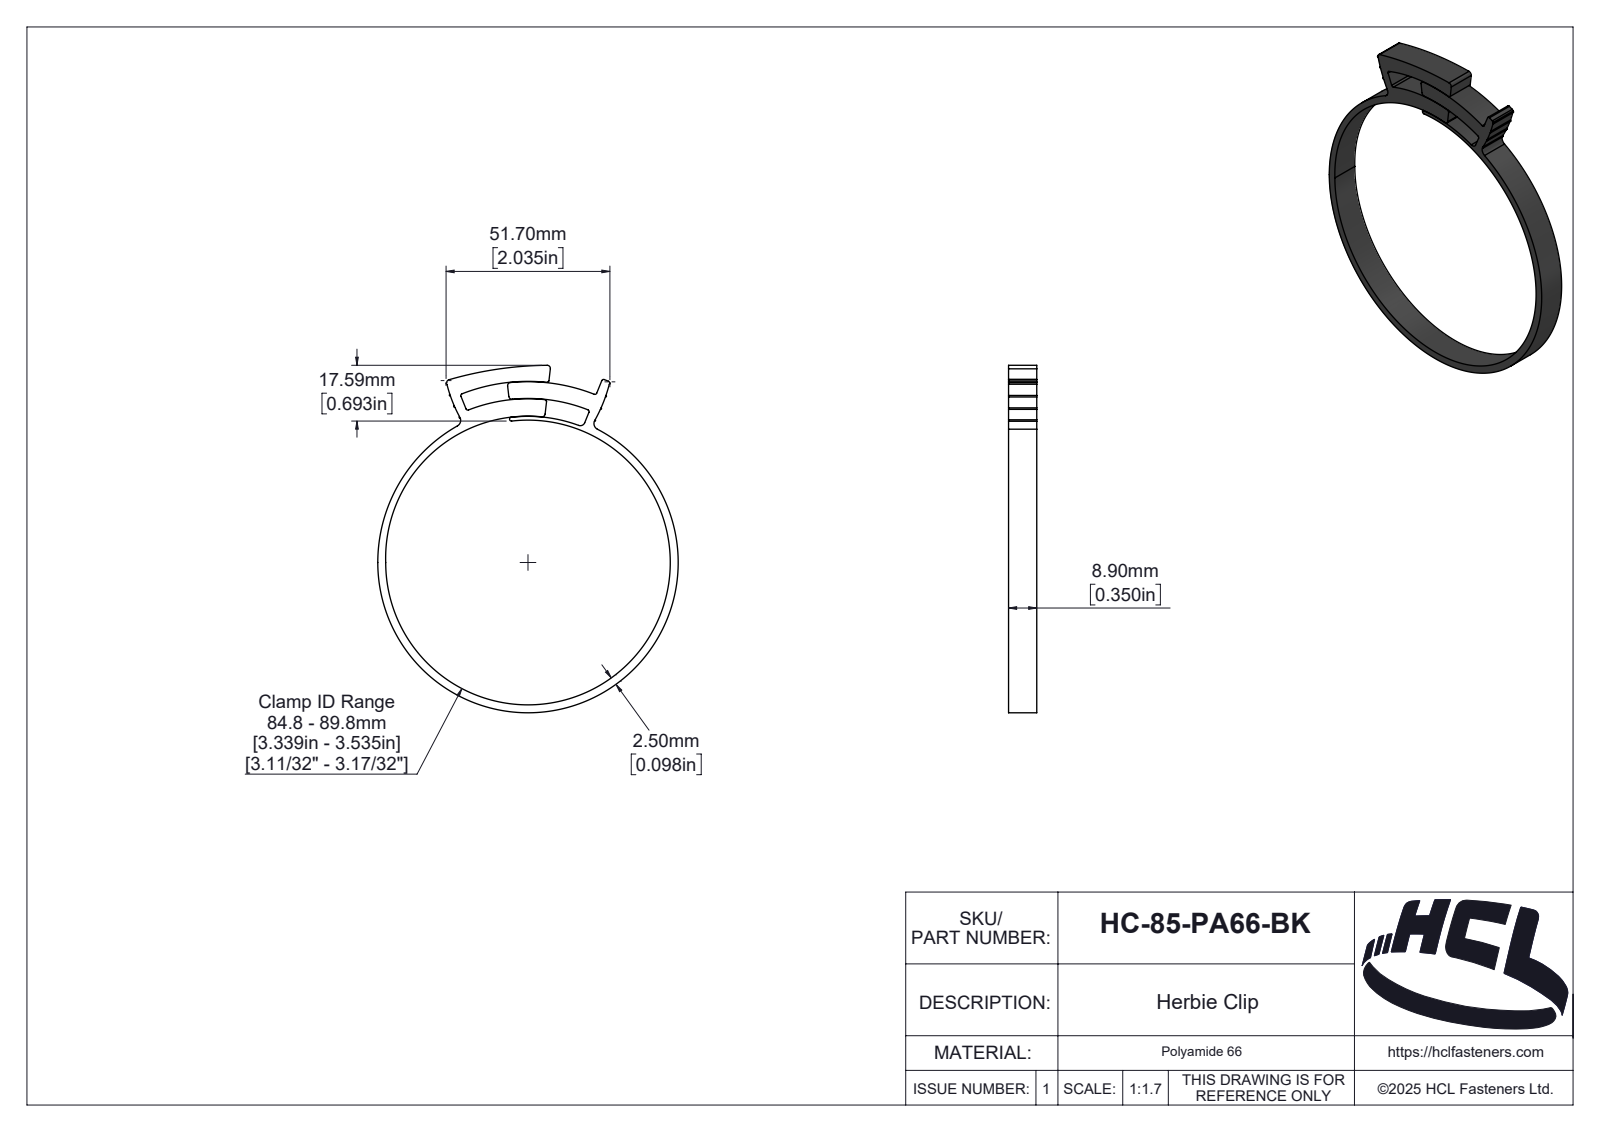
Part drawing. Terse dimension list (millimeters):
name: HC-85-PA66-BK
written by: SolidWorks 2025 (AUTOMOTIVE_DESIGN)
unit: mm
bodies: 1 solid, 161 faces (13 planar, 99 cylindrical, 49 other)
size: 109.59 × 94.8 × 8.9
volume: 10 330 mm³; area: 9 254 mm²
rounds: 8× R0.25, 7× R0.6, 5× R1, 2× R2, 1× R0.17, 1× R0.67, 1× R0.84, 1× R0.89
face distances: 8.9
